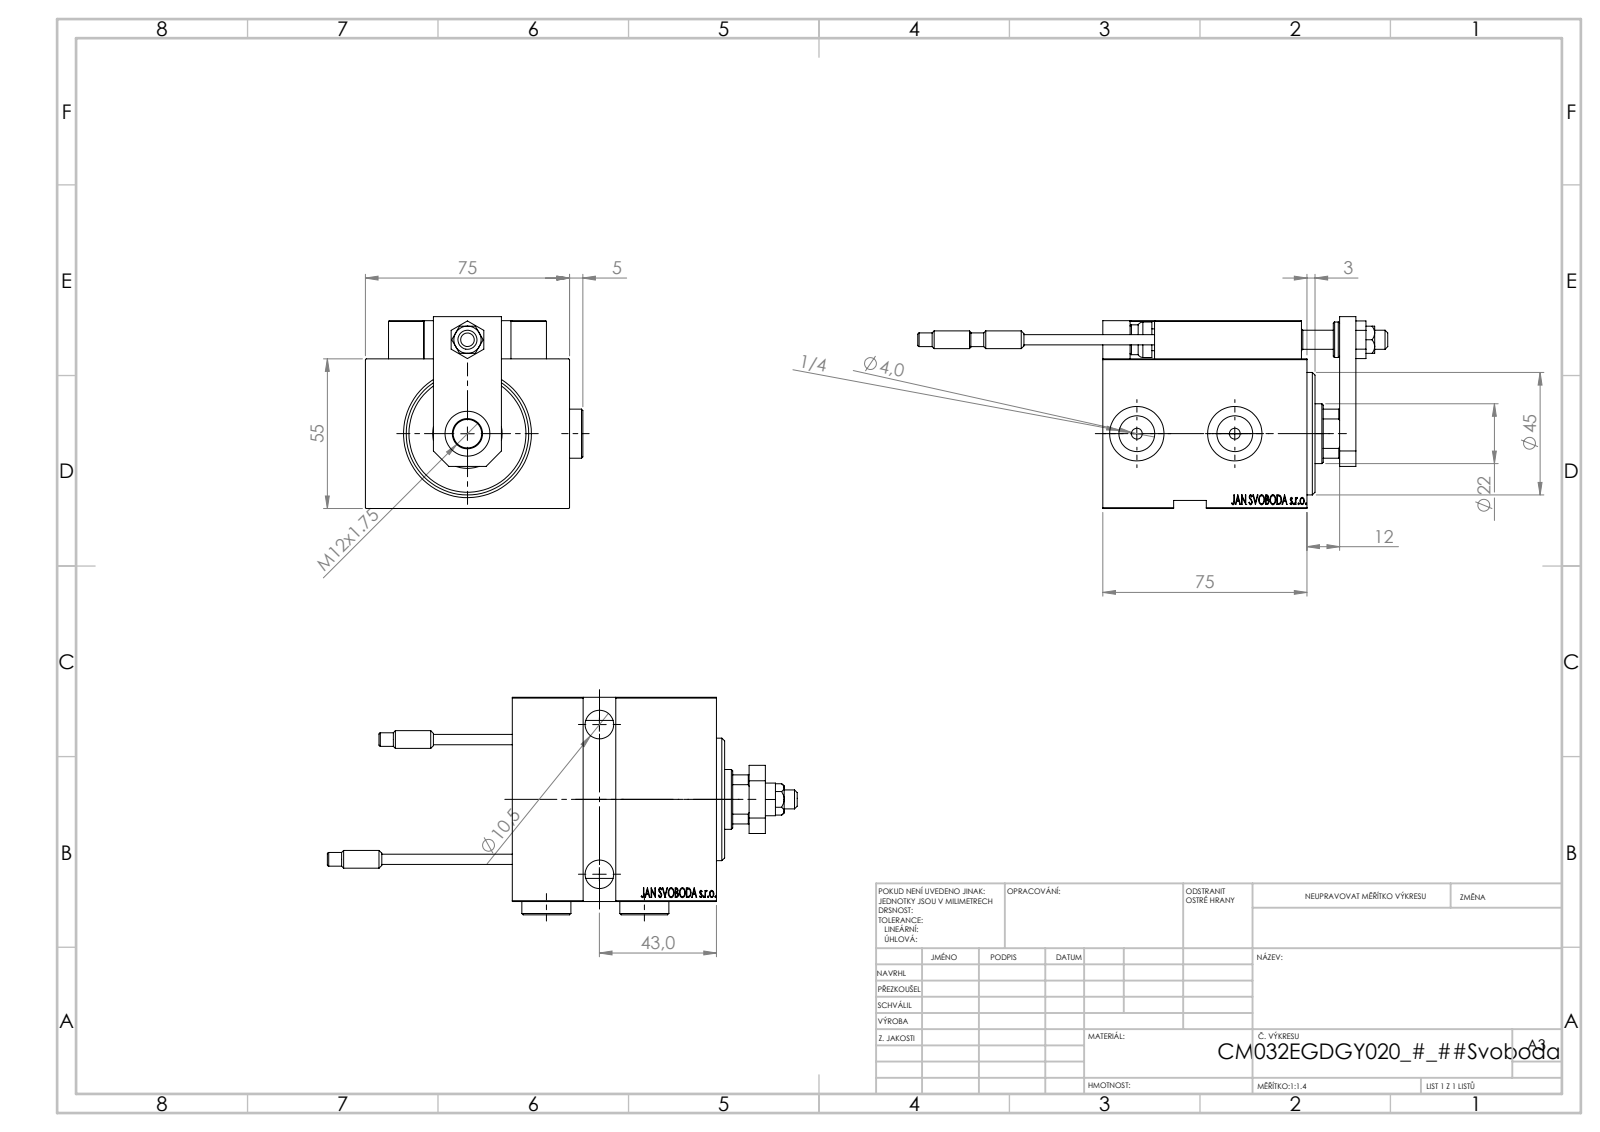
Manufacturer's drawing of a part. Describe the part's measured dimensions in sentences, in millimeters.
The part is named "V450CM_E_Body; MAGNET; ALLEN BOLT D5; KONCOVKA_Y (+7 more)". Its 3-D file was written by "SolidWorks 2019 (CONFIG_CONTROL_DESIGN)". It is 26 solids with 1358 faces: 605 planar, 196 cylindrical and 557 other. Overall it measures 172.7 by 79.9 by 70.5 millimeters. Its volume is 337 600 cubic millimeters and its surface area 82 528 square millimeters. Round holes: 6 of diameter 4, 5 of diameter 8, 4 of diameter 3.2, 3 of diameter 10.5, 3 of diameter 16.5, 2 of diameter 5, 2 of diameter 13.16, 2 of diameter 20, 1 of diameter 7, 1 of diameter 22, 1 of diameter 25.5, 1 of diameter 32. Round bosses or shafts: 4 of diameter 5, 2 of diameter 18, 2 of diameter 6.5, 2 of diameter 3.8, 1 of diameter 34, 1 of diameter 13, 1 of diameter 11. Partial cylindrical surfaces (rounded edges, fillets, slot ends): 30 of radius 0.3, 2 of radius 3, 1 of radius 10.5. The main face-to-face distances are 75, 55, 10, 14, 3, 5, 12, 25, 65, 69. The hole center spacings are 11.37, 20, 27.07, 29.59, 29.69, 32.18, 34.83, 36.06.
